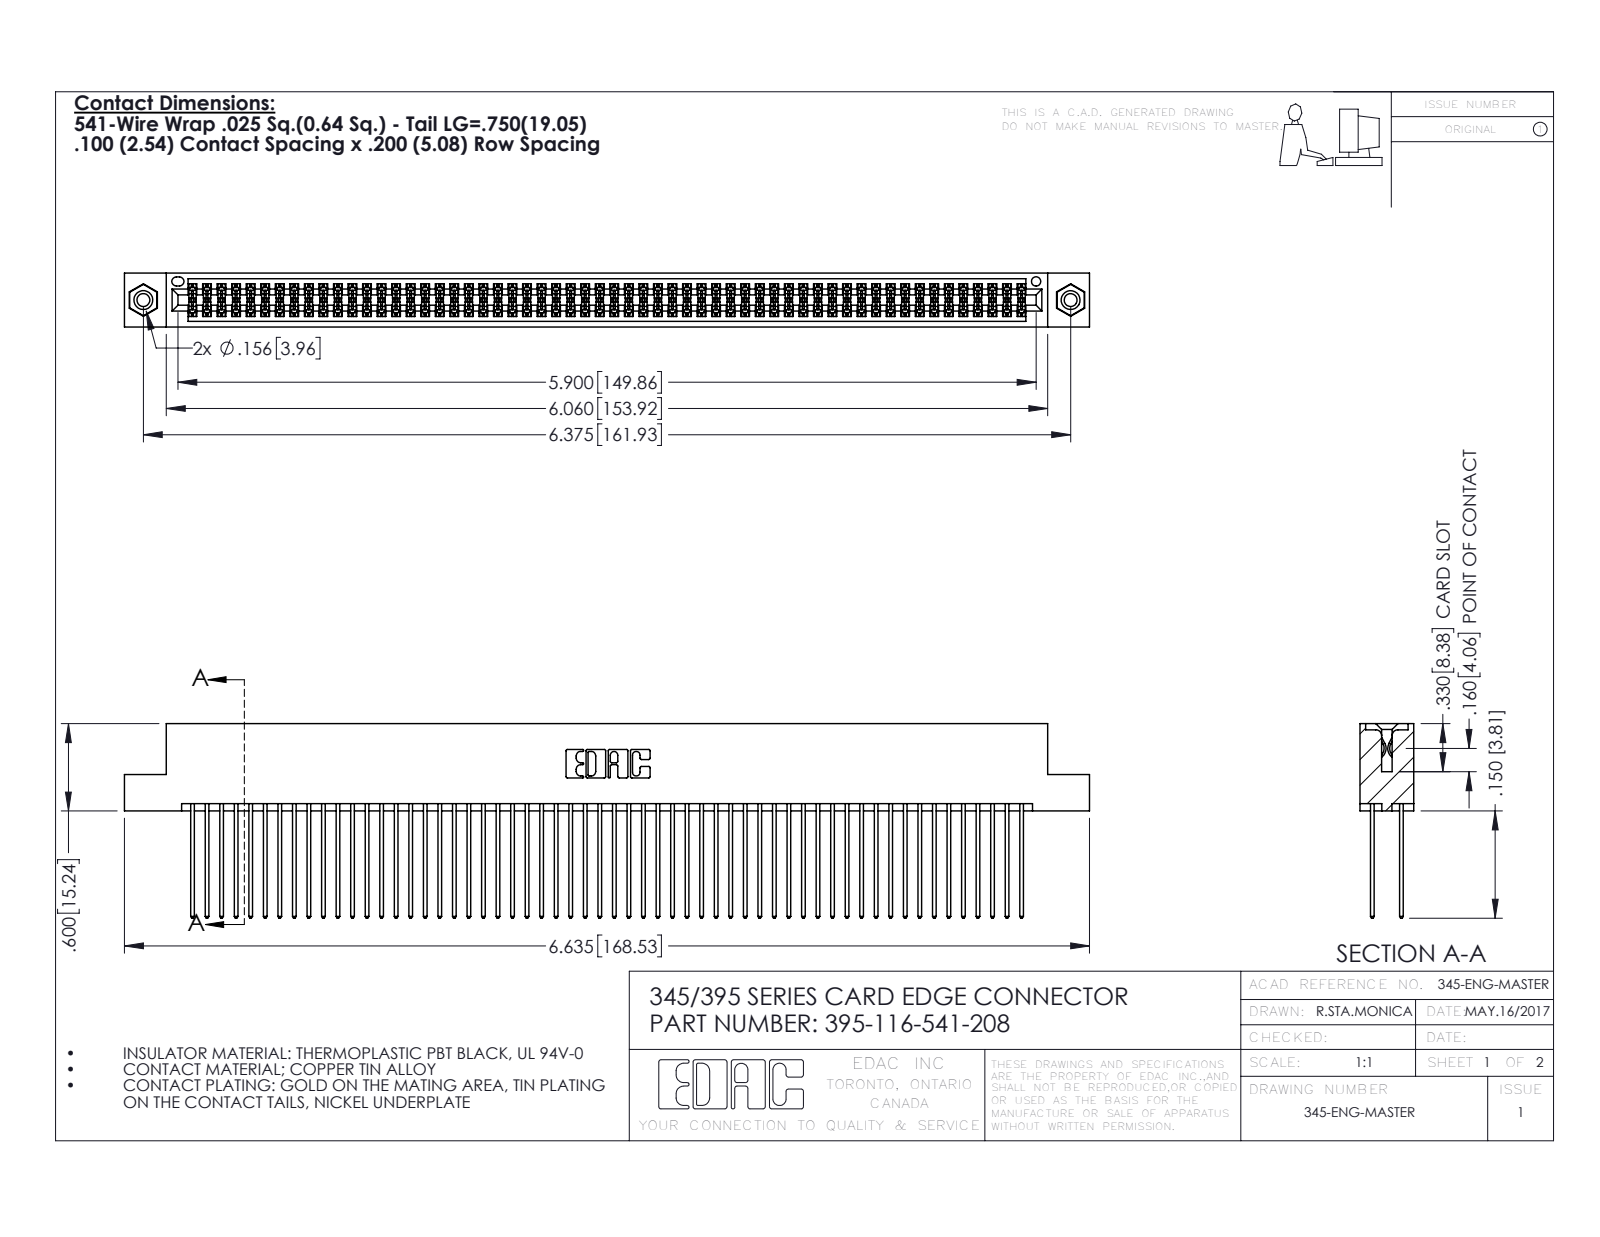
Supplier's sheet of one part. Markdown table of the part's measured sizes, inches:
| quantity | value |
| --- | --- |
| part name | 395-116-541-208; 345 Part_Flush Mounting Lugs - 0.156 Dia-TI; 345-250-001_345-250-003-102; 345-292-001_345-293-141 |
| STEP written by | SolidWorks 2016 (CONFIG_CONTROL_DESIGN) |
| units | inches |
| bodies | 119 solids, 5986 faces (3940 planar, 2030 cylindrical, 16 other) |
| overall size | 6.635 × 1.337 × 0.37 |
| volume | 1.048 in³ |
| surface area | 44.71 in² |
| round holes (diameter × count) | 0.089 × 2, 0.125 × 2, 0.156 × 2, 0.064 × 1 |
| round bosses / shafts (diameter × count) | 0.155 × 2 |
| partial cylindrical surfaces (radius × count) | 0.006 × 174, 0.01 × 116, 0.01 × 22, 0.007 × 6, 0.031 × 6, 0.026 × 3, 0.014 × 2, 0.019 × 2 |
| main face-to-face distances | 0.072, 0.298, 0.2, 0.098, 0.272, 0.025, 0.225, 0.37, 0.175, 0.149 |
| hole center spacings | 0.27, 6.139, 6.375 |
